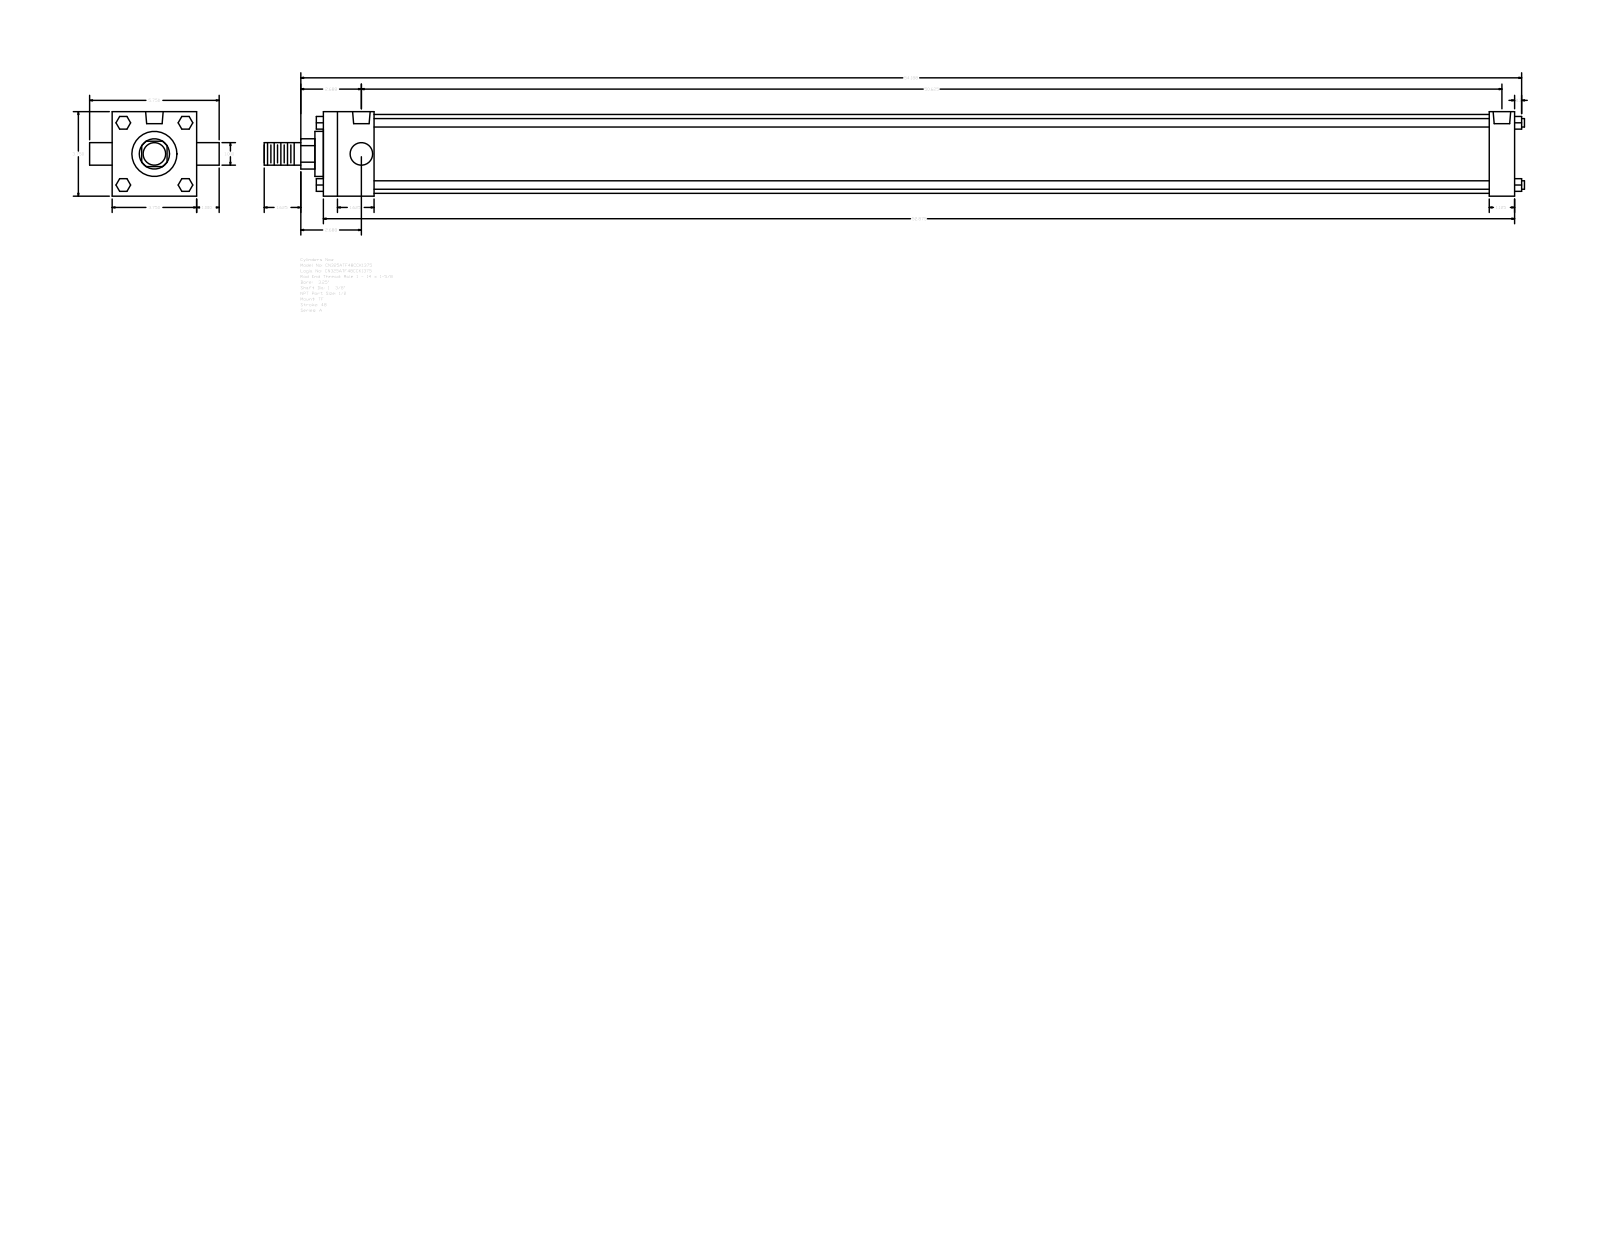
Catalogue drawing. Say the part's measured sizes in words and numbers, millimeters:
The part is named "A_TF__0325_1.375". Its 3-D file was written by "GSSL Pune (CONFIG_CONTROL_DESIGN)". It is 0 solids with 120 faces: 92 planar, 28 cylindrical and 0 other. Overall it measures 1420.81 by 146.05 by 95.25 millimeters. Round holes: 3 of diameter 8.73, 2 of diameter 19.77. Round bosses or shafts: 4 of diameter 9.53, 2 of diameter 25.4, 1 of diameter 88.9, 1 of diameter 50.8, 1 of diameter 34.92. Partial cylindrical surfaces (rounded edges, fillets, slot ends): 1 of radius 17.06. The main face-to-face distances are 95.24, 1343.02, 57.15, 1314.45, 1257.3, 1285.87, 28.57, 66.67, 9.52, 1323.97. The hole center spacings are 3.18, 1282.7, 1279.52, 1285.88.
